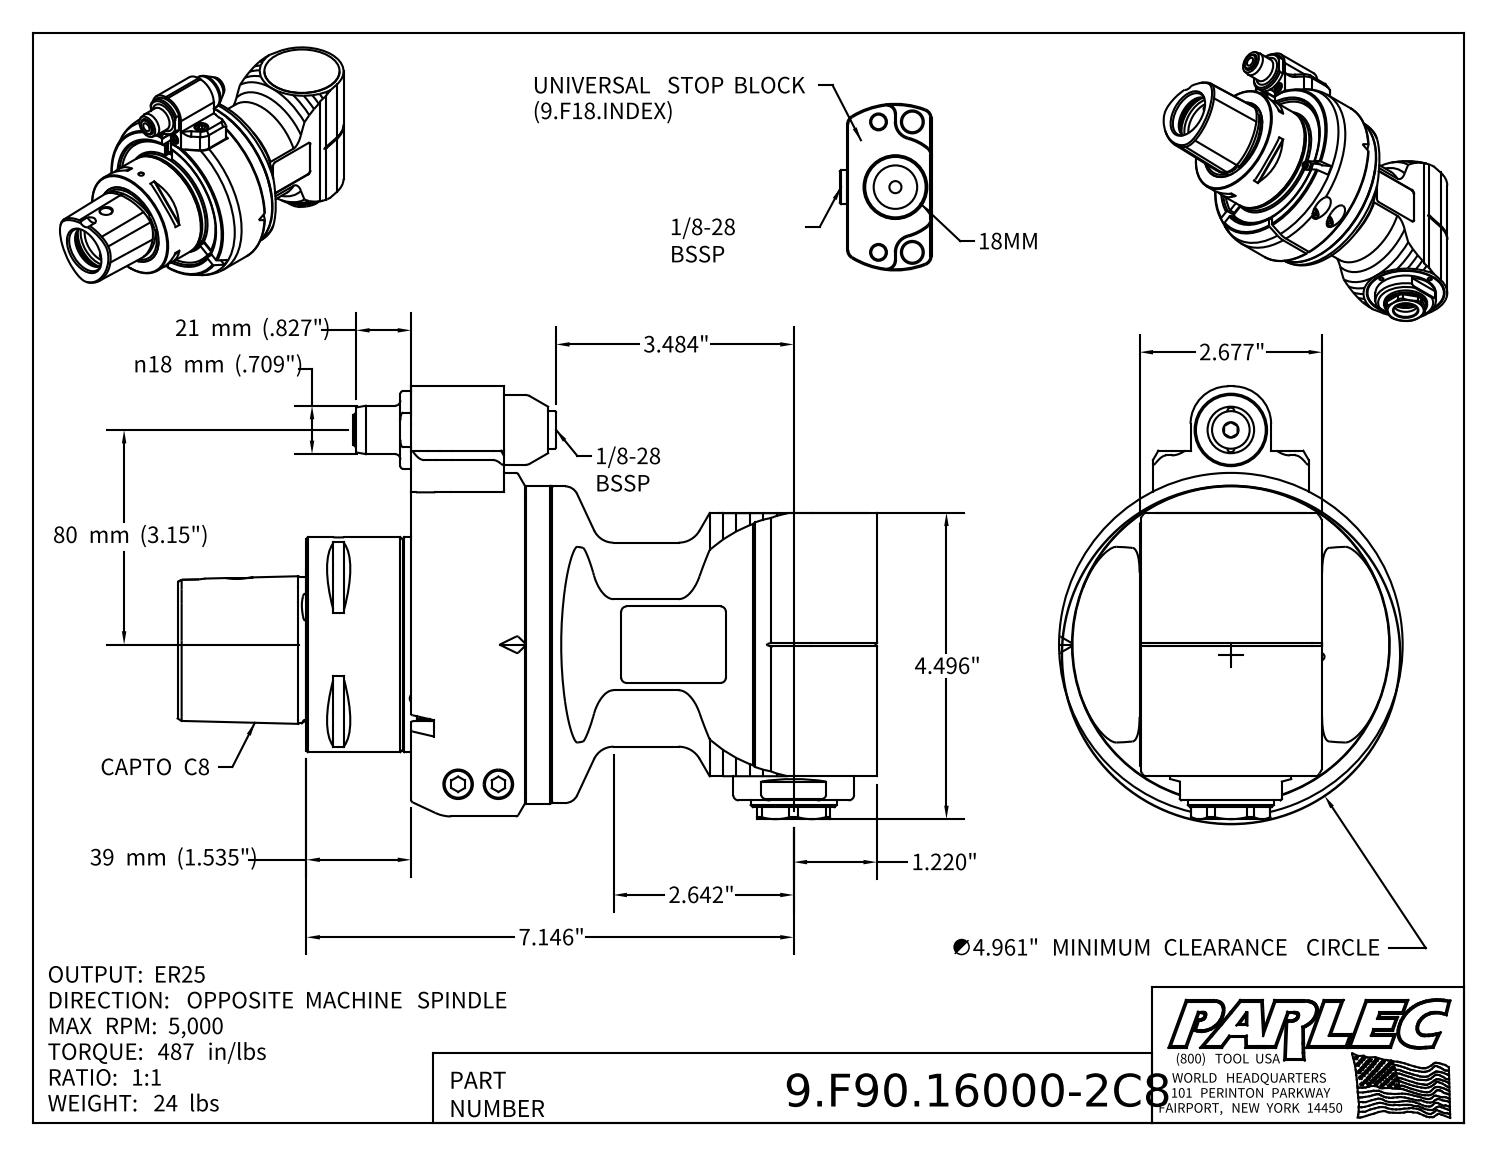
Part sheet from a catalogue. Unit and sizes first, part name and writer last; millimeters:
Units: millimetres
Overall size (bounding box): 260.5 × 161.2 × 128
Round holes (diameter × count): ⌀10.5 ×20, ⌀3.2 ×4, ⌀5 ×4, ⌀2.6 ×2, ⌀4.2 ×2, ⌀5.3 ×2, ⌀8 ×2, ⌀10.4 ×2, ⌀11 ×2, ⌀12.5 ×2, ⌀18 ×2, ⌀2.5 ×1
Round bosses / shafts (diameter × count): ⌀10 ×4, ⌀6 ×4, ⌀2.5 ×2, ⌀128 ×1, ⌀118.4 ×1, ⌀118 ×1, ⌀99 ×1, ⌀80 ×1
Partial cylindrical surfaces — rounded edges, fillets, slot ends (radius × count): R2 ×12, R4 ×4, R0.4 ×2, R0.5 ×2, R1 ×2, R8 ×2, R14 ×2, R6 ×1
Main face-to-face distances: 0.5, 35.5, 1, 35, 2, 6.5, 32.5, 34, 1.5, 5
Hole centre spacings: 46.8, 56.3, 66.1, 92.6, 93.5, 45.3, 81.8, 13
Volume: 1 586 000 mm³ · Surface area: 192 700 mm²
Bodies: 5 solids, 593 faces (246 planar, 141 cylindrical, 206 other)
Part name (STEP PRODUCT): 9.F90.16000-2C8; 9_F90_16000
STEP written by: Autodesk Inventor 2025 (AUTOMOTIVE_DESIGN)
